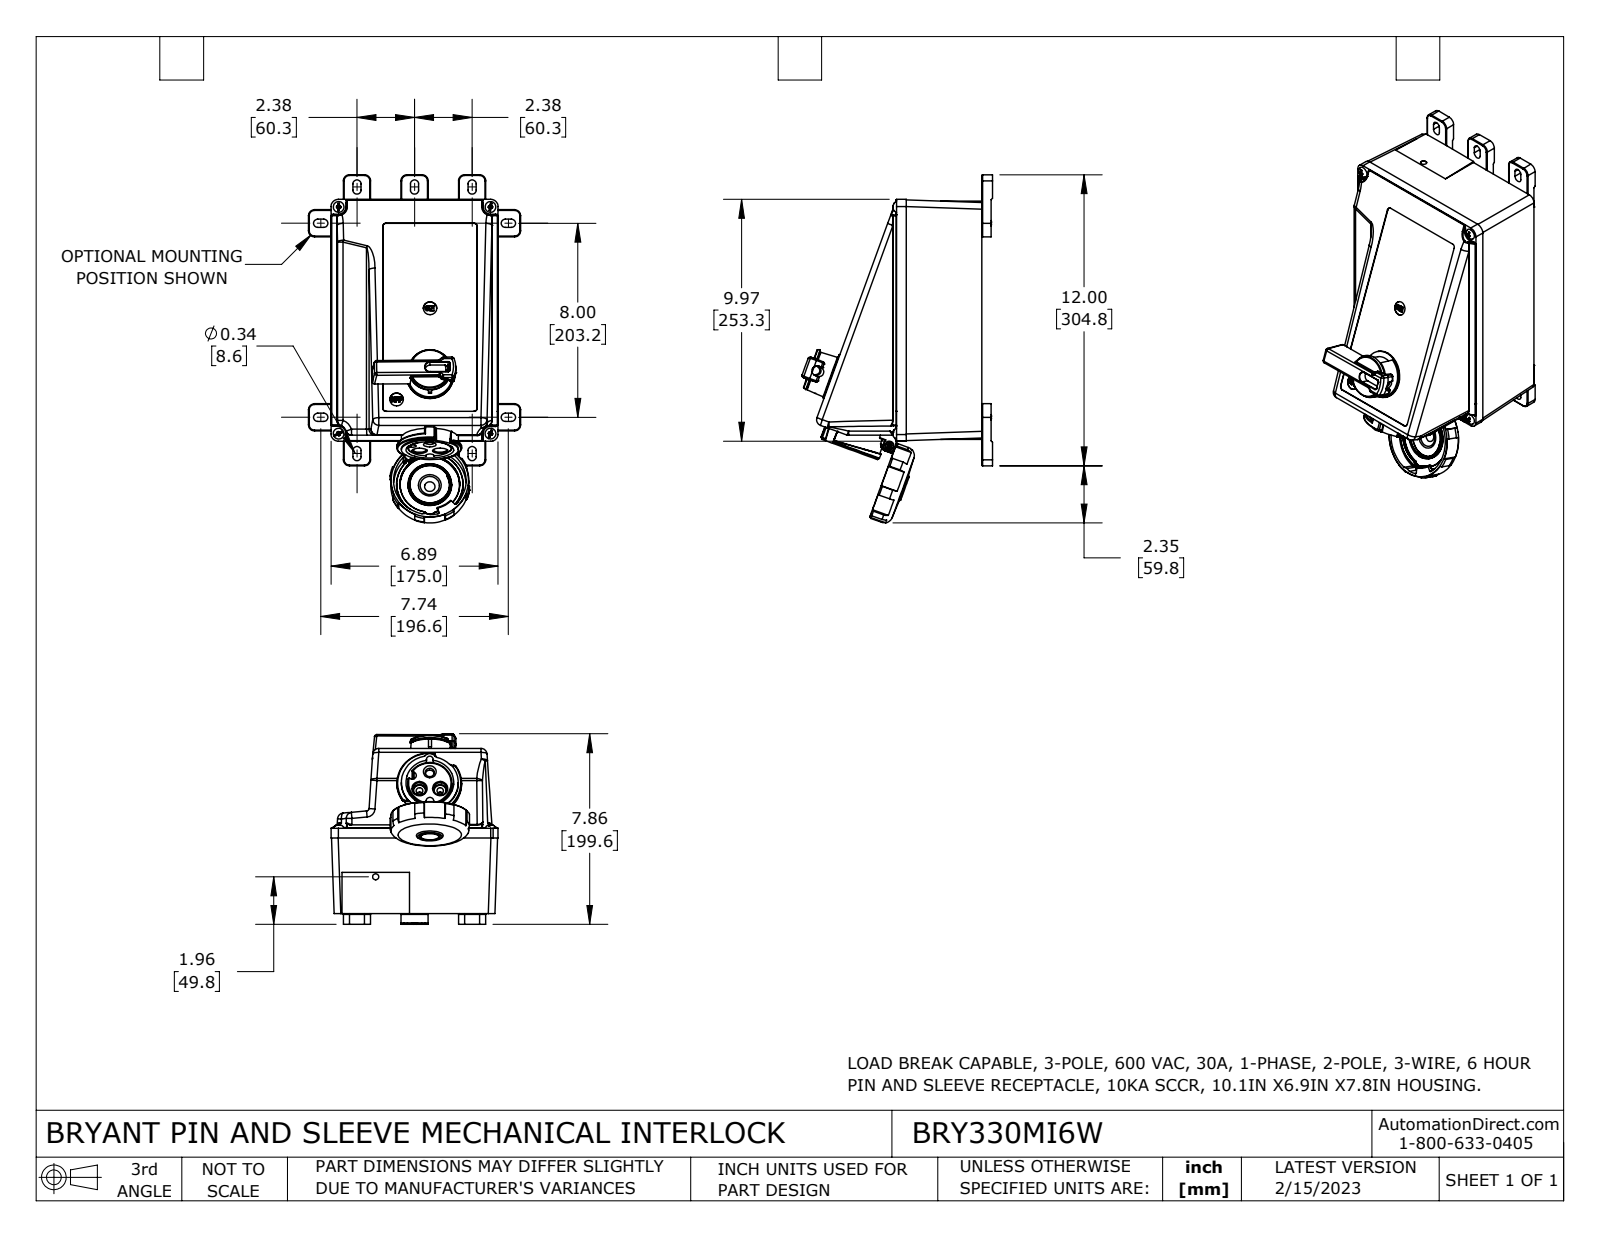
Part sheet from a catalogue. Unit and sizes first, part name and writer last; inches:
Units: inches
Overall size (bounding box): 14.354 × 7.858 × 6.891
Round holes (diameter × count): ⌀0.281 ×5, ⌀0.078 ×4, ⌀0.157 ×2, ⌀0.56 ×2, ⌀0.101 ×1, ⌀0.139 ×1, ⌀0.159 ×1, ⌀0.25 ×1, ⌀0.27 ×1, ⌀0.66 ×1, ⌀0.773 ×1, ⌀0.86 ×1
Round bosses / shafts (diameter × count): ⌀0.263 ×2, ⌀0.121 ×2, ⌀2.742 ×1, ⌀2.352 ×1, ⌀1.92 ×1, ⌀1.85 ×1, ⌀1.83 ×1, ⌀1.794 ×1
Partial cylindrical surfaces — rounded edges, fillets, slot ends (radius × count): R0.015 ×124, R0.03 ×54, R0.08 ×30, R0.25 ×24, R0.09 ×17, R0.01 ×16, R0.02 ×13, R0.075 ×12
Main face-to-face distances: 0.12, 0.175, 9.655, 4.75, 9.83, 4.168, 4.156, 0.15, 0.38, 0.035
Hole centre spacings: 0.7, 0.7, 0.788, 0.852, 2.685, 3.307, 4.75, 8
Volume: 336.8 in³ · Surface area: 469.1 in²
Bodies: 10 solids, 2048 faces (727 planar, 669 cylindrical, 652 other)
Part name (STEP PRODUCT): BRY330MI6W
STEP written by: SolidWorks 2021 (CONFIG_CONTROL_DESIGN)
